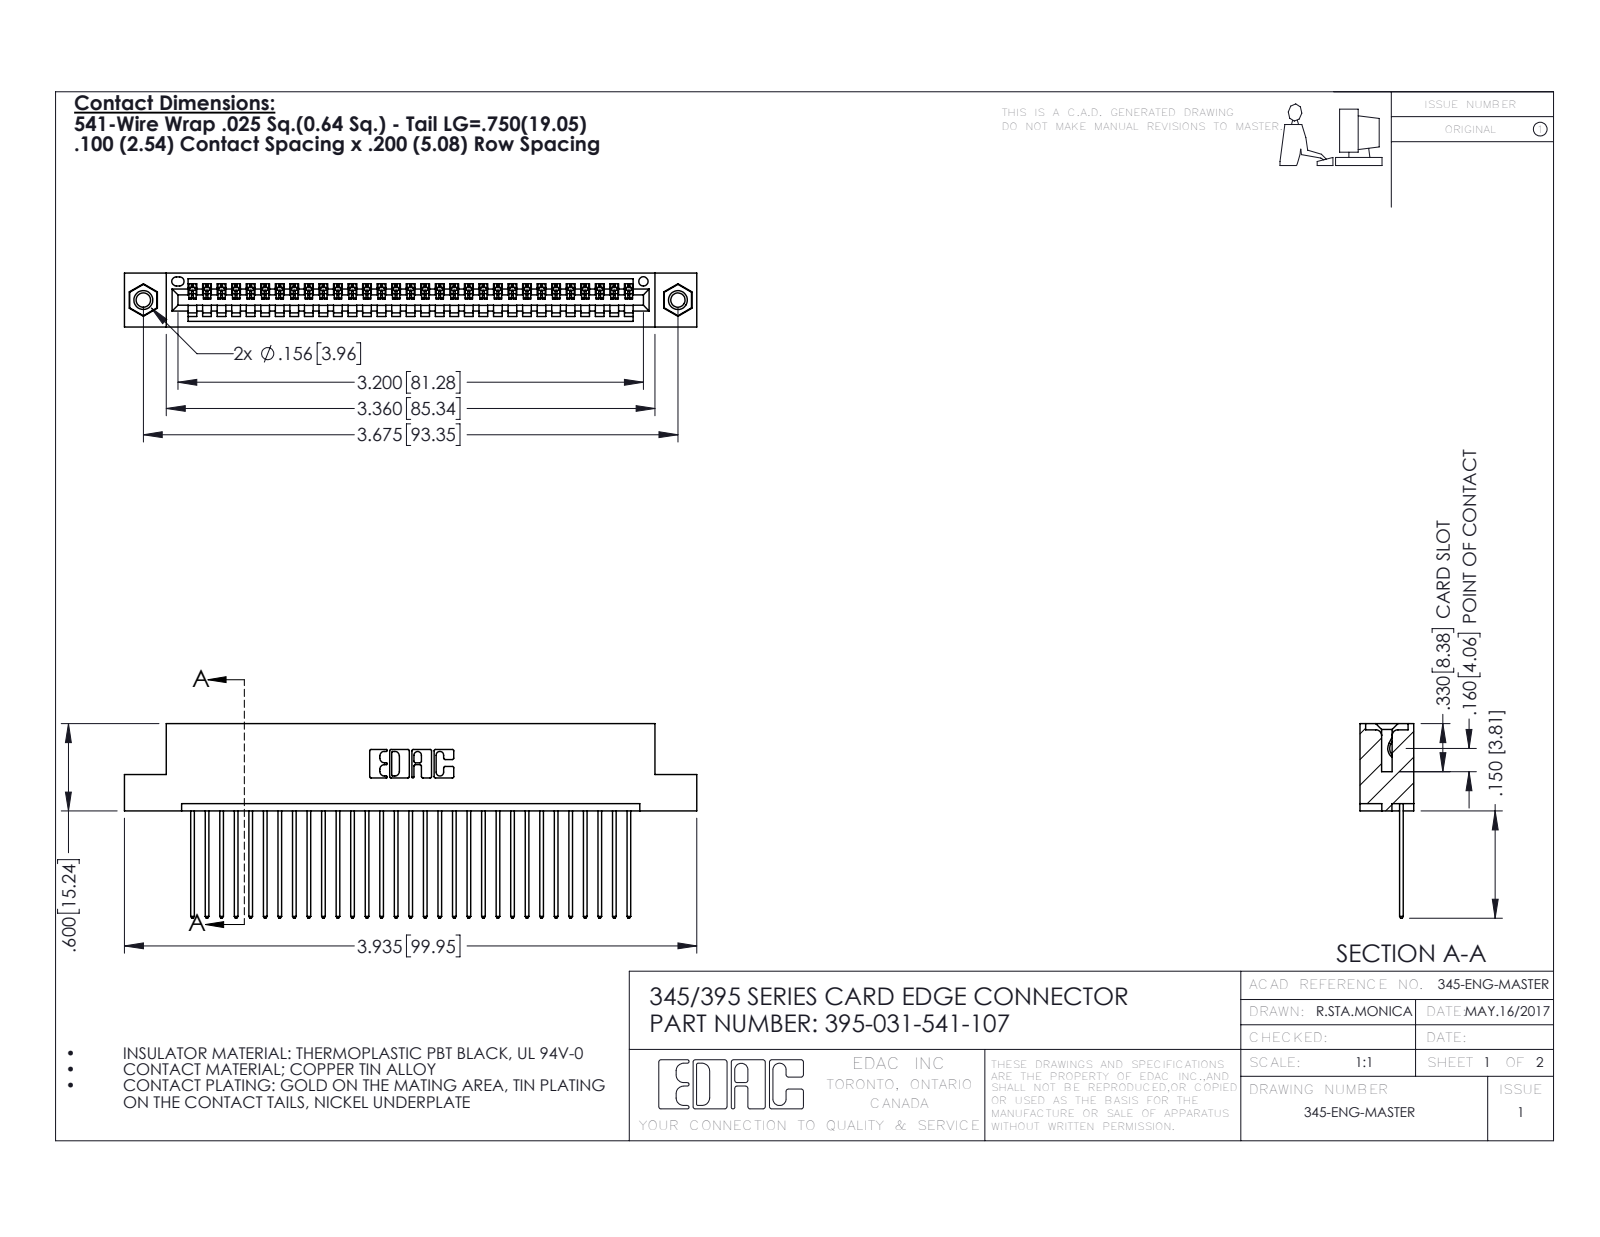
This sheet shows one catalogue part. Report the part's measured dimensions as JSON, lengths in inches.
{"part_name": "345-292-001_345-293-141; 345 Part_Flush Mounting Lugs - 0.156 Dia-TI; 345-250-001_345-250-005-103; 395-031-541-107", "step_written_by": "SolidWorks 2016 (CONFIG_CONTROL_DESIGN)", "units": "inches", "bodies": {"solids": 34, "faces": 1984, "planar": 1352, "cylindrical": 616, "other": 16}, "overall_size": [3.935, 1.337, 0.37], "volume_in3": 0.579, "surface_area_in2": 20.3, "round_holes": [[0.098, 2], [0.125, 2], [0.156, 2], [0.064, 1]], "round_bosses_or_shafts": [[0.155, 2]], "partial_cylinders_radius": [[0.006, 62], [0.01, 62], [0.01, 22], [0.007, 6], [0.031, 6], [0.026, 3], [0.031, 2], [0.04, 2]], "face_to_face_distances": [0.072, 0.298, 0.2, 0.37, 0.098, 0.272, 0.025, 0.225, 0.149, 0.072], "hole_center_spacings": [0.27, 3.44, 3.675]}
